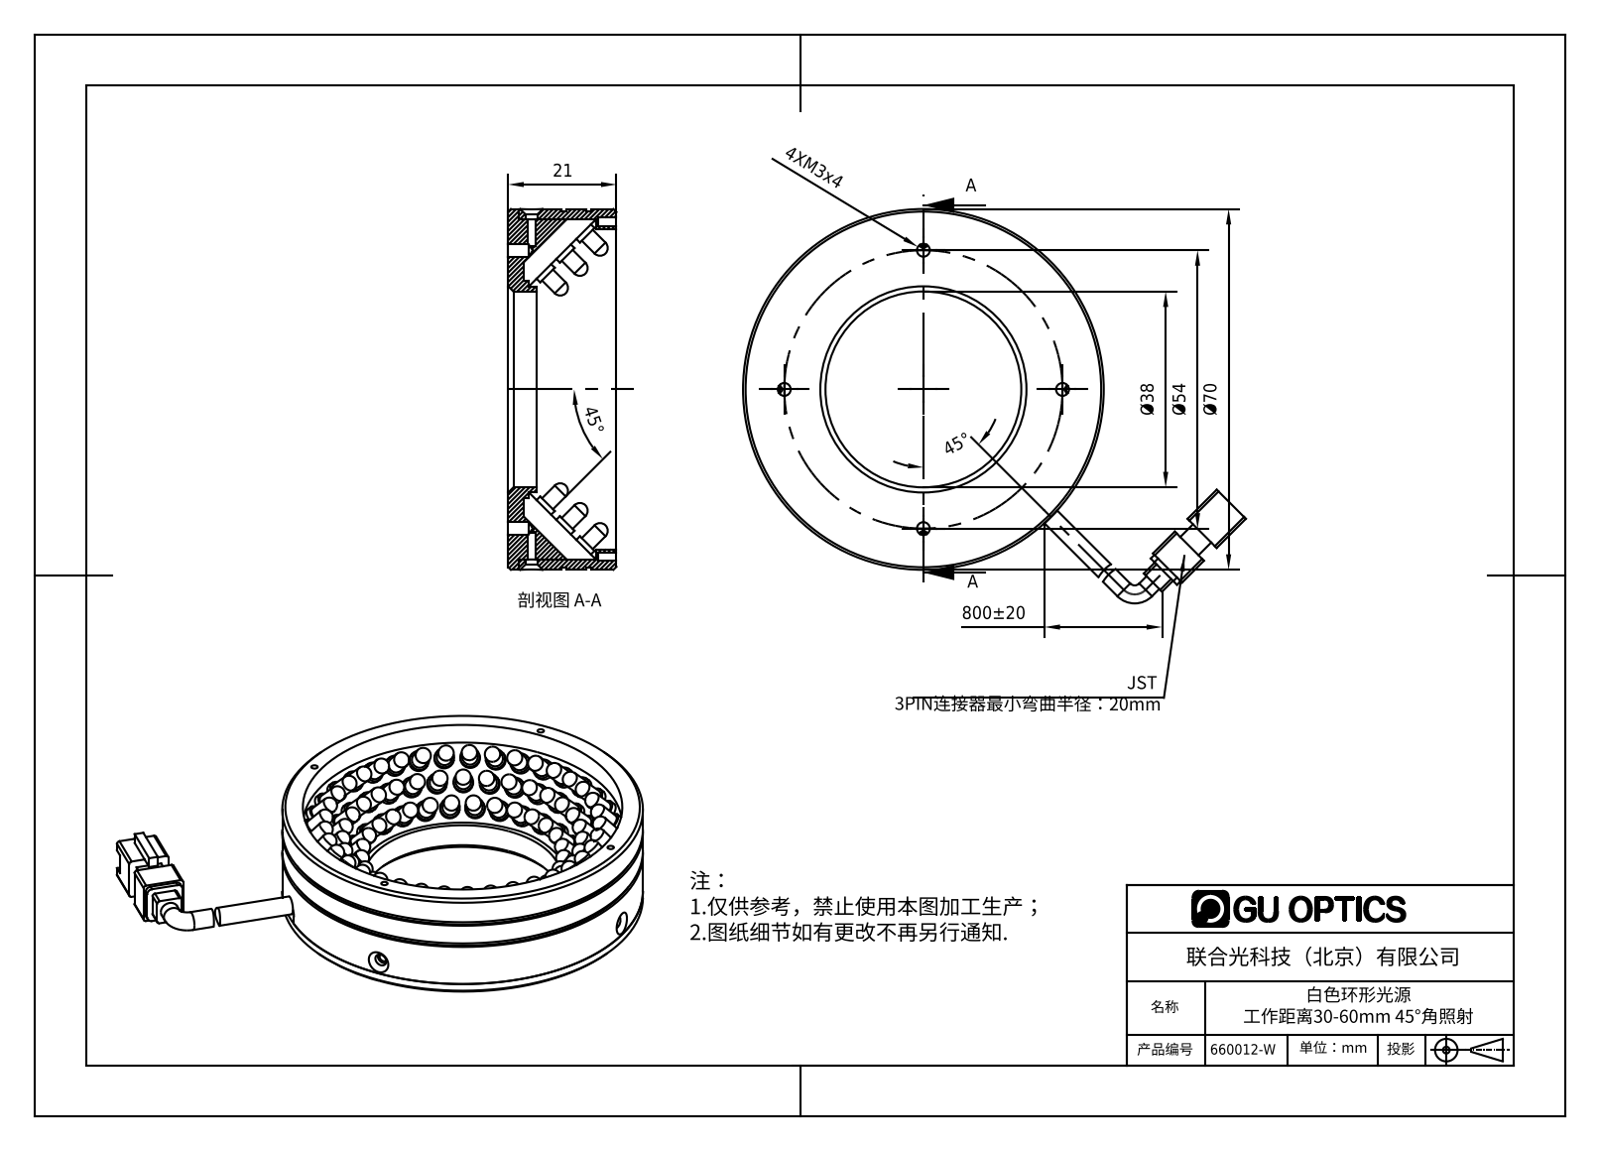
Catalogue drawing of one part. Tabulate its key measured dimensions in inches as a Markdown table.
| quantity | value |
| --- | --- |
| part name | 660012-W |
| STEP written by | SolidWorks 2016 (AUTOMOTIVE_DESIGN) |
| units | inches |
| bodies | 103 solids, 1900 faces (1251 planar, 494 cylindrical, 155 other) |
| overall size | 3.842 × 3.013 × 0.827 |
| volume | 1.814 in³ |
| surface area | 54.48 in² |
| round holes (diameter × count) | 0.049 × 4, 0.098 × 4, 0.118 × 3, 0.063 × 2, 0.094 × 2, 1.496 × 1, 2.441 × 1 |
| round bosses / shafts (diameter × count) | 0.15 × 98, 0.118 × 97, 0.138 × 2, 2.756 × 1, 2.717 × 1, 2.598 × 1, 1.654 × 1, 1.575 × 1 |
| partial cylindrical surfaces (radius × count) | 0.02 × 8, 0.039 × 4, 0.065 × 1, 0.197 × 1 |
| main face-to-face distances | 0.039, 0.079, 0.118, 0.748, 0.157, 0.827, 0.669, 0.709, 0.02, 0.551 |
| hole center spacings | 1.663, 0.217, 1.063, 1.28, 1.503, 1.809, 2.343, 2.126 |
